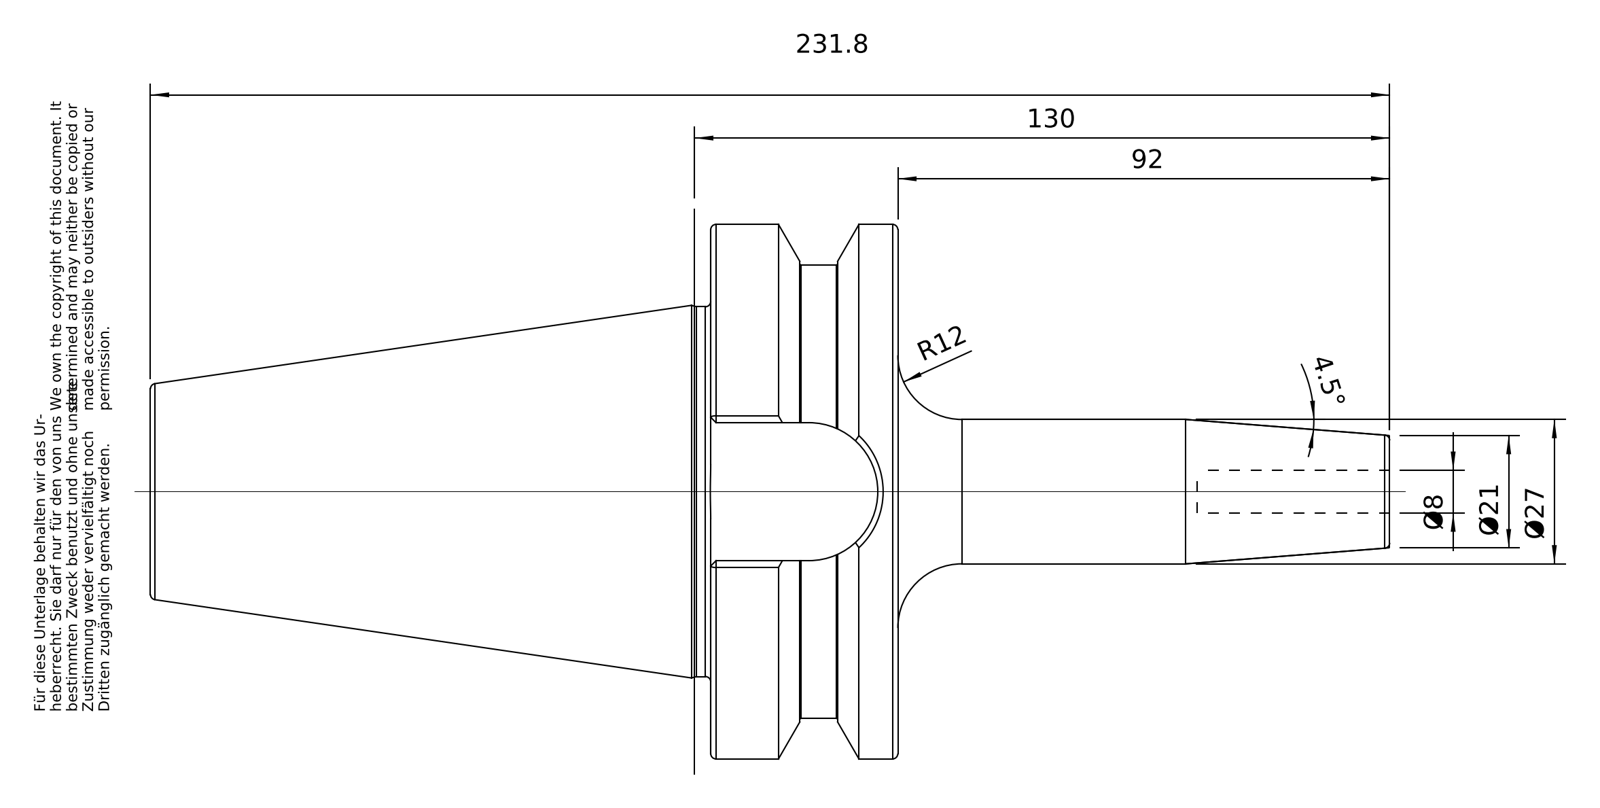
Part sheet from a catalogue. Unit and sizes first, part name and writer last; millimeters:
Units: millimetres
Overall size (bounding box): 231.8 × 99.97 × 99.97
Round holes (diameter × count): ⌀8 ×1, ⌀20.75 ×1, ⌀25.02 ×1, ⌀25.7 ×1
Round bosses / shafts (diameter × count): ⌀99.97 ×1, ⌀84.75 ×1, ⌀69.15 ×1, ⌀27 ×1, ⌀24.01 ×1
Partial cylindrical surfaces — rounded edges, fillets, slot ends (radius × count): R12.9 ×1
Main face-to-face distances: 35, 70.4, 104.8, 139.8, 25.8, 231.8, 127, 92, 48, 56.8
Volume: 517 552 mm³ · Surface area: 59 583 mm²
Bodies: 1 solid, 96 faces (26 planar, 22 cylindrical, 48 other)
Part name (STEP PRODUCT): 50-644-08
STEP written by: PRO/ENGINEER BY PARAMETRIC TECHNOLOGY CORPORATION, 2010430 (CONFIG_CONTROL_DESIGN)
